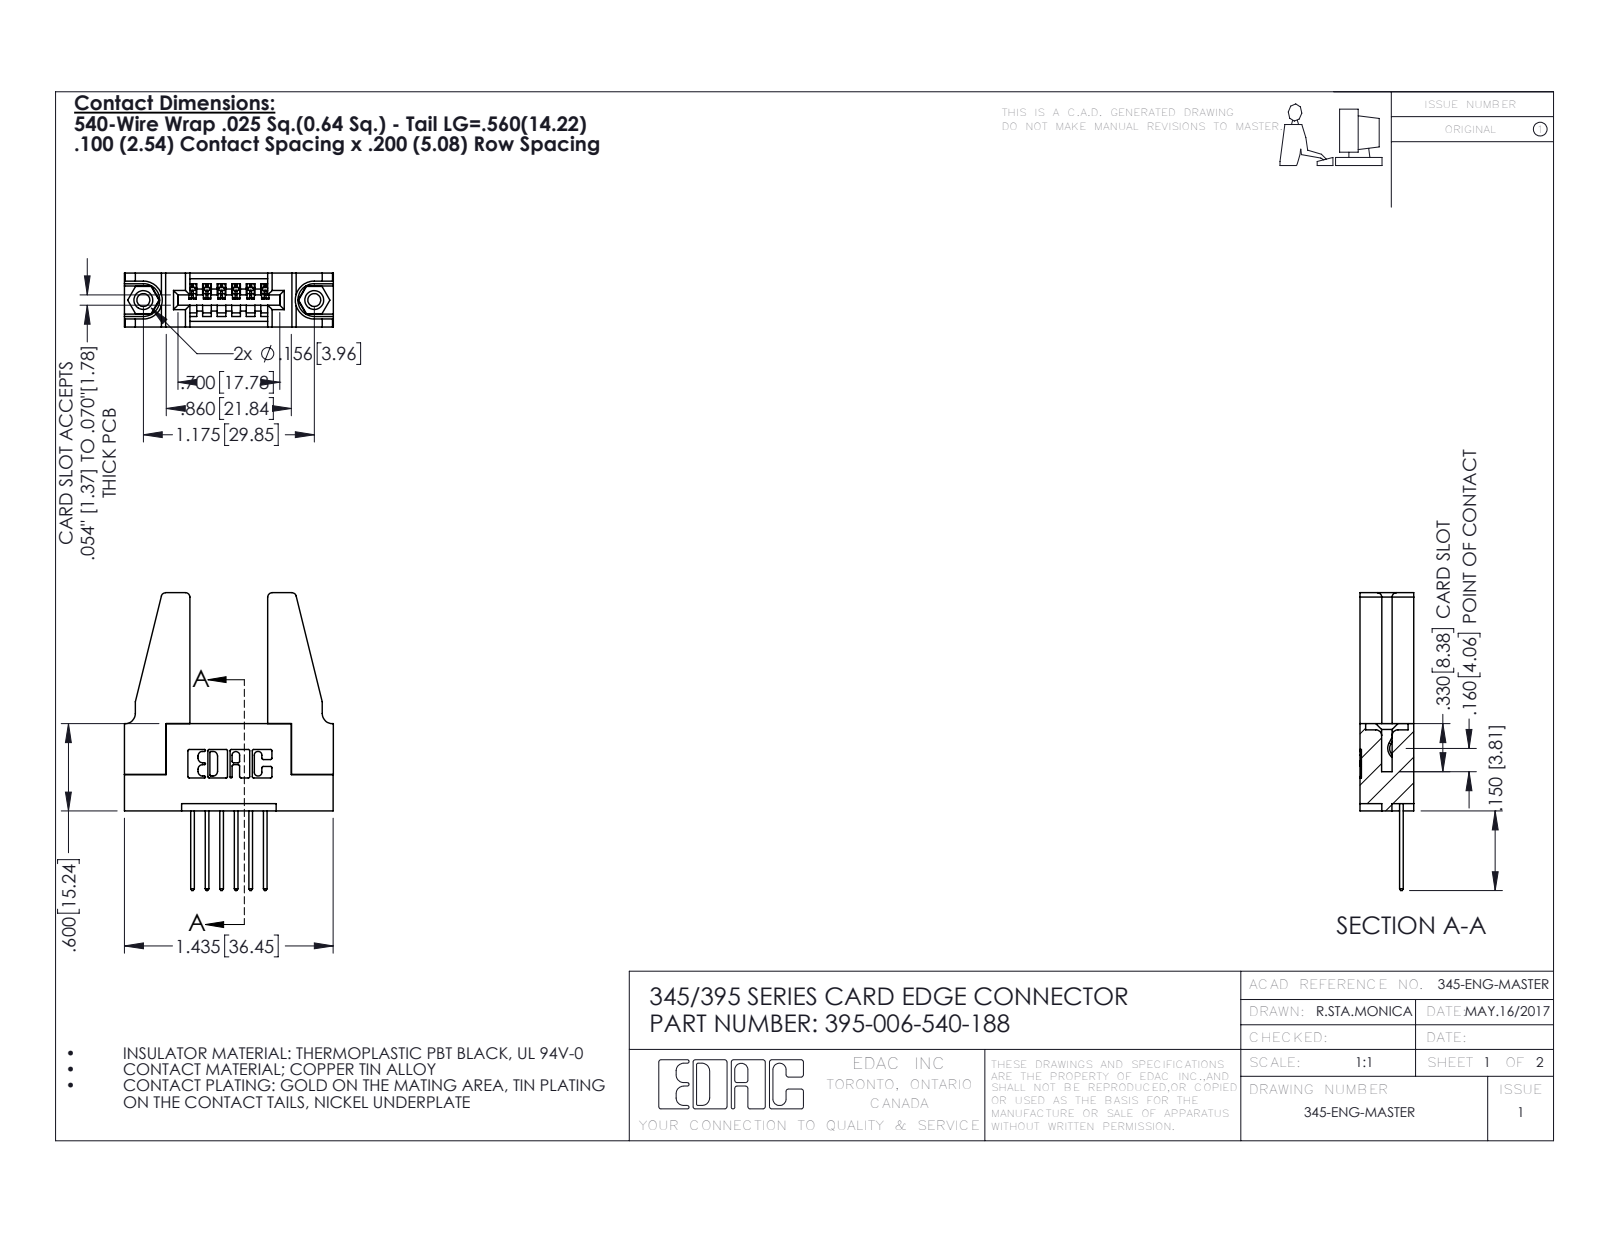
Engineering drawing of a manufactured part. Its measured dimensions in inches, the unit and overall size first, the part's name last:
Units: inches
Overall size (bounding box): 2.047 × 1.436 × 0.37
Round holes (diameter × count): ⌀0.089 ×2, ⌀0.125 ×2, ⌀0.156 ×2, ⌀0.064 ×1
Round bosses / shafts (diameter × count): ⌀0.155 ×2
Partial cylindrical surfaces — rounded edges, fillets, slot ends (radius × count): R0.01 ×22, R0.006 ×12, R0.01 ×12, R0.03 ×8, R0.007 ×6, R0.031 ×6, R0.026 ×3, R0.031 ×2
Main face-to-face distances: 0.37, 0.2, 0.072, 0.298, 0.698, 0.098, 0.272, 0.025, 0.15, 0.148
Hole centre spacings: 0.27, 0.946, 1.175
Volume: 0.392 in³ · Surface area: 10.73 in²
Bodies: 11 solids, 598 faces (392 planar, 190 cylindrical, 16 other)
Part name (STEP PRODUCT): 395-006-540-188; 345 Part_Flush Mounting Lugs - 0.156 Dia-TH; 345-250-001_345-250-001-102; 345-220-078_345-220-088 (+1 more)
STEP written by: SolidWorks 2016 (CONFIG_CONTROL_DESIGN)
